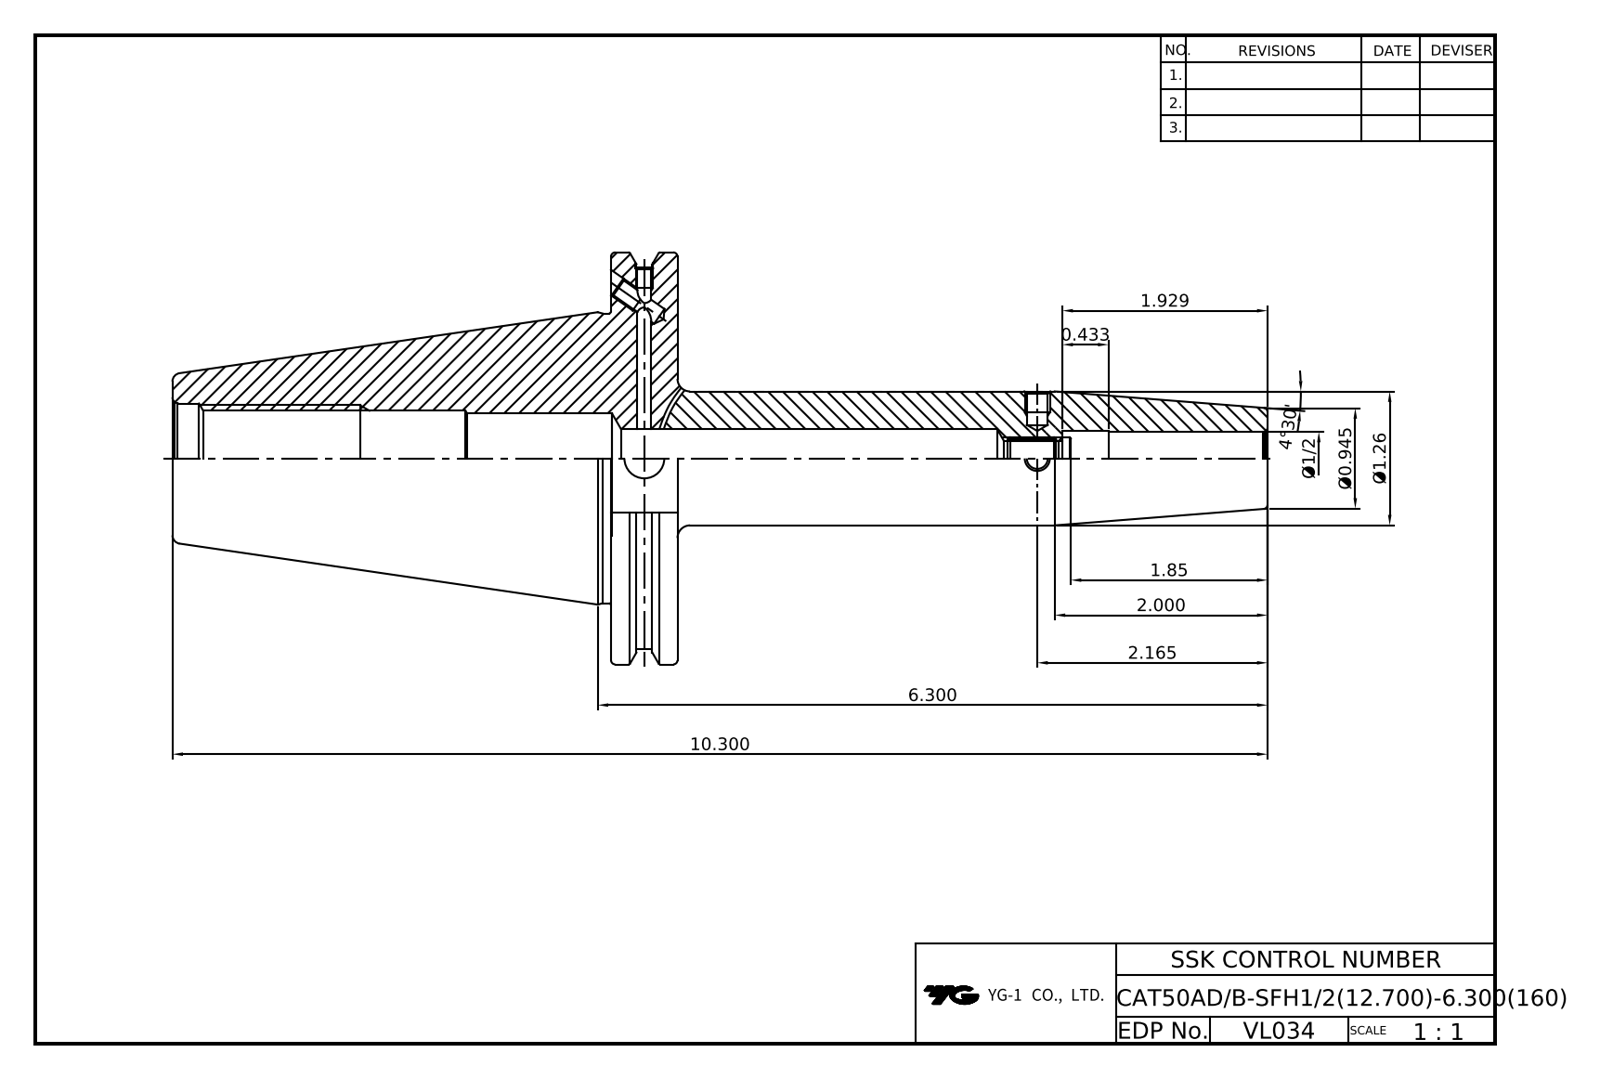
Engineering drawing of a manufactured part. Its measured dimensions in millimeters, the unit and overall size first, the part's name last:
Units: millimetres
Overall size (bounding box): 261.6 × 98.42 × 94.69
Round holes (diameter × count): ⌀3.24 ×2, ⌀4.13 ×2, ⌀4.2 ×2, ⌀5 ×2, ⌀8.92 ×1, ⌀9.53 ×1, ⌀12.7 ×1, ⌀13.9 ×1, ⌀14 ×1, ⌀21.97 ×1, ⌀26.2 ×1
Round bosses / shafts (diameter × count): ⌀98.42 ×1, ⌀91.29 ×1, ⌀69.25 ×1, ⌀32 ×1
Main face-to-face distances: 15.88, 104.77, 120.65, 73.03, 25.9, 261.6, 156.83, 140.95, 110.82, 6.05
Volume: 407 522 mm³ · Surface area: 63 498 mm²
Bodies: 1 solid, 86 faces (37 planar, 27 cylindrical, 22 other)
Part name (STEP PRODUCT): LO-CAT50ADB-SFH12.7-160
STEP written by: Autodesk Inventor 2025 (AUTOMOTIVE_DESIGN)
